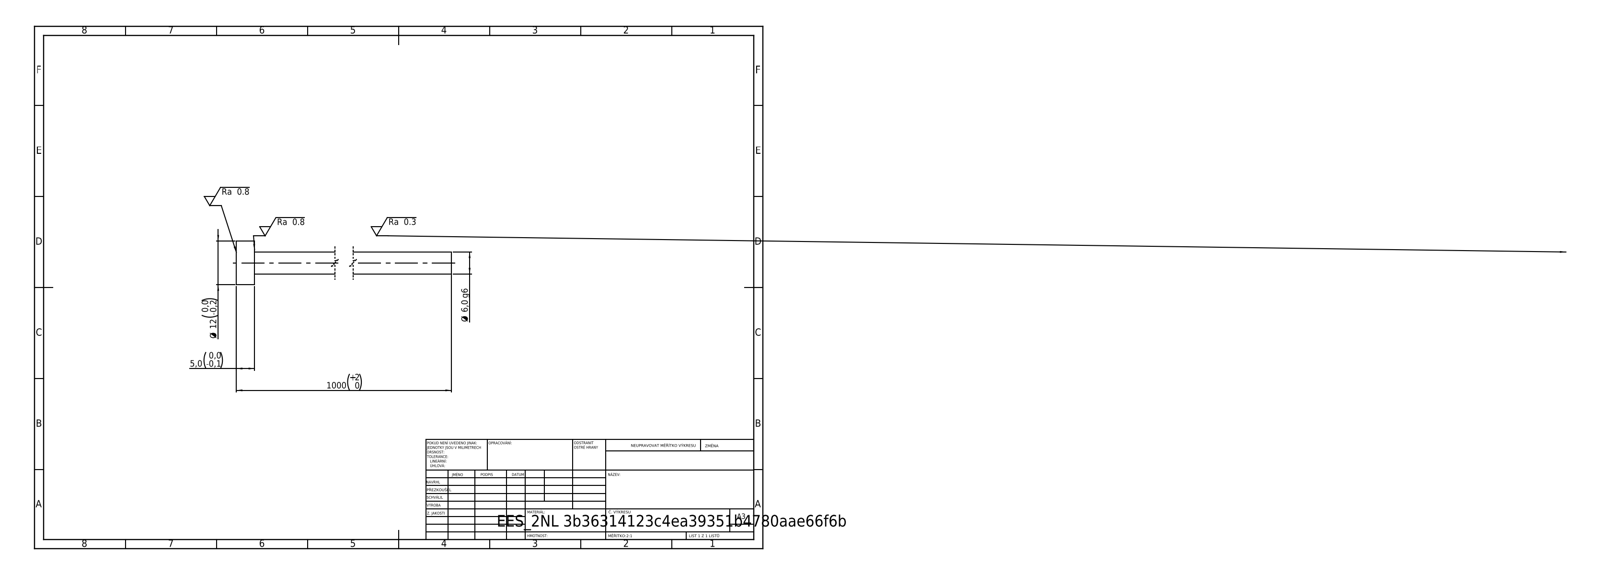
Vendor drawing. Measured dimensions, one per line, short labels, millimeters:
written by: SolidWorks 2019 (CONFIG_CONTROL_DESIGN)
unit: mm
bodies: 1 solid, 7 faces (3 planar, 4 cylindrical, 0 other)
size: 1000 × 12 × 12
volume: 28 698 mm³; area: 19 170 mm²
bosses: 1× ⌀12, 1× ⌀6
face distances: 5, 1000, 995
